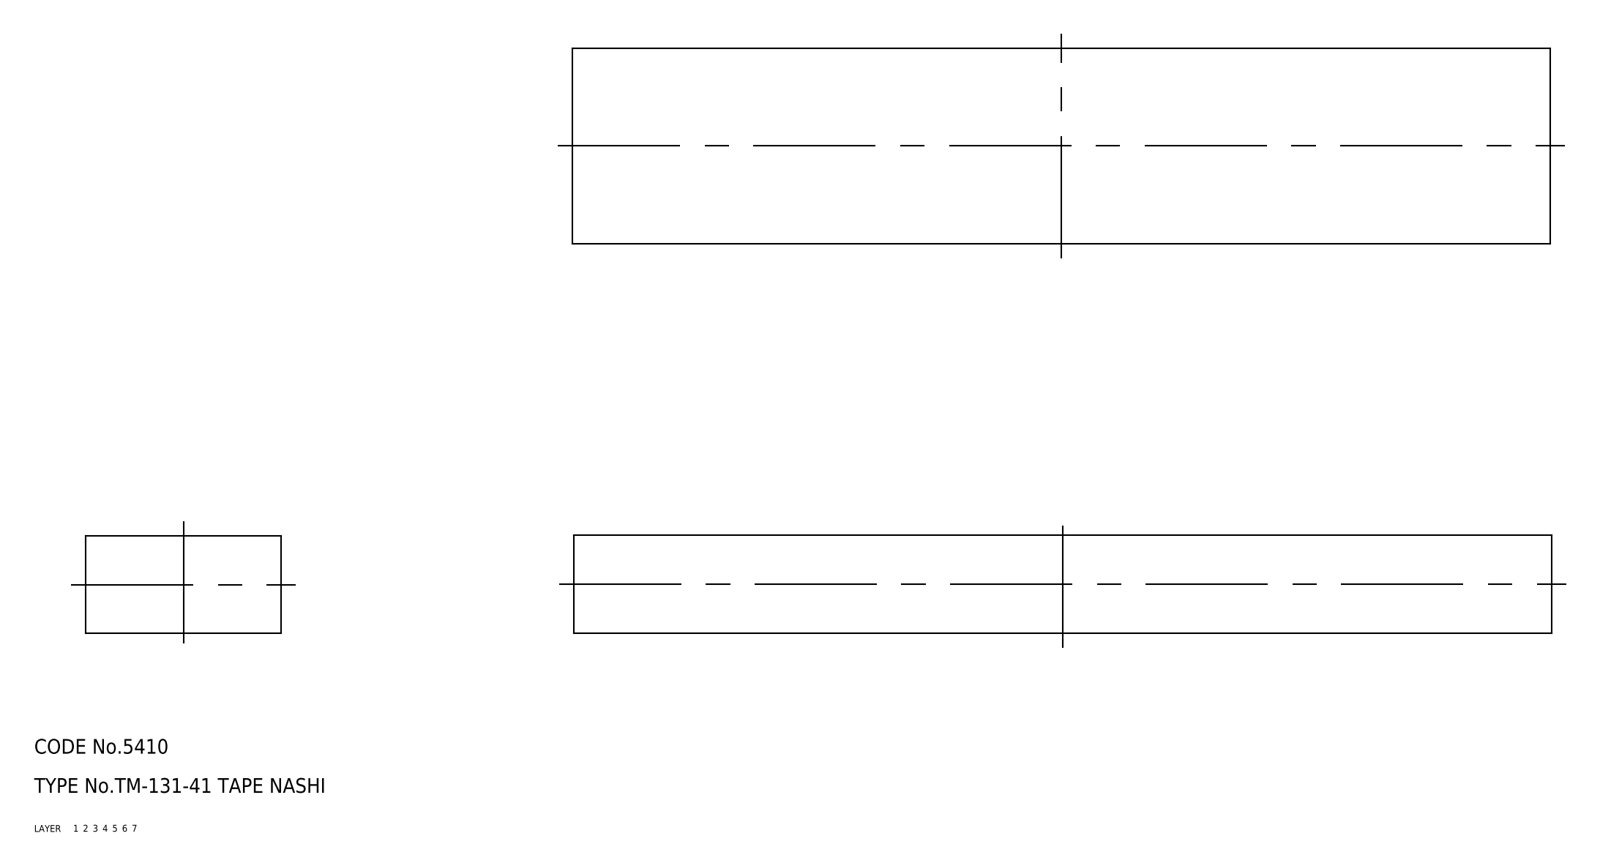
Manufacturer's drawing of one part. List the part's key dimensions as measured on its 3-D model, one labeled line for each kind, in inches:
Part name (STEP PRODUCT): rubber foam
STEP written by: CADfix (AUTOMOTIVE_DESIGN)
Units: inches
Bodies: 1 solid, 6 faces (0 planar, 0 cylindrical, 6 other)
Overall size (bounding box): 7.874 × 1.575 × 0.787
Volume: 9.764 in³ · Surface area: 39.68 in²
